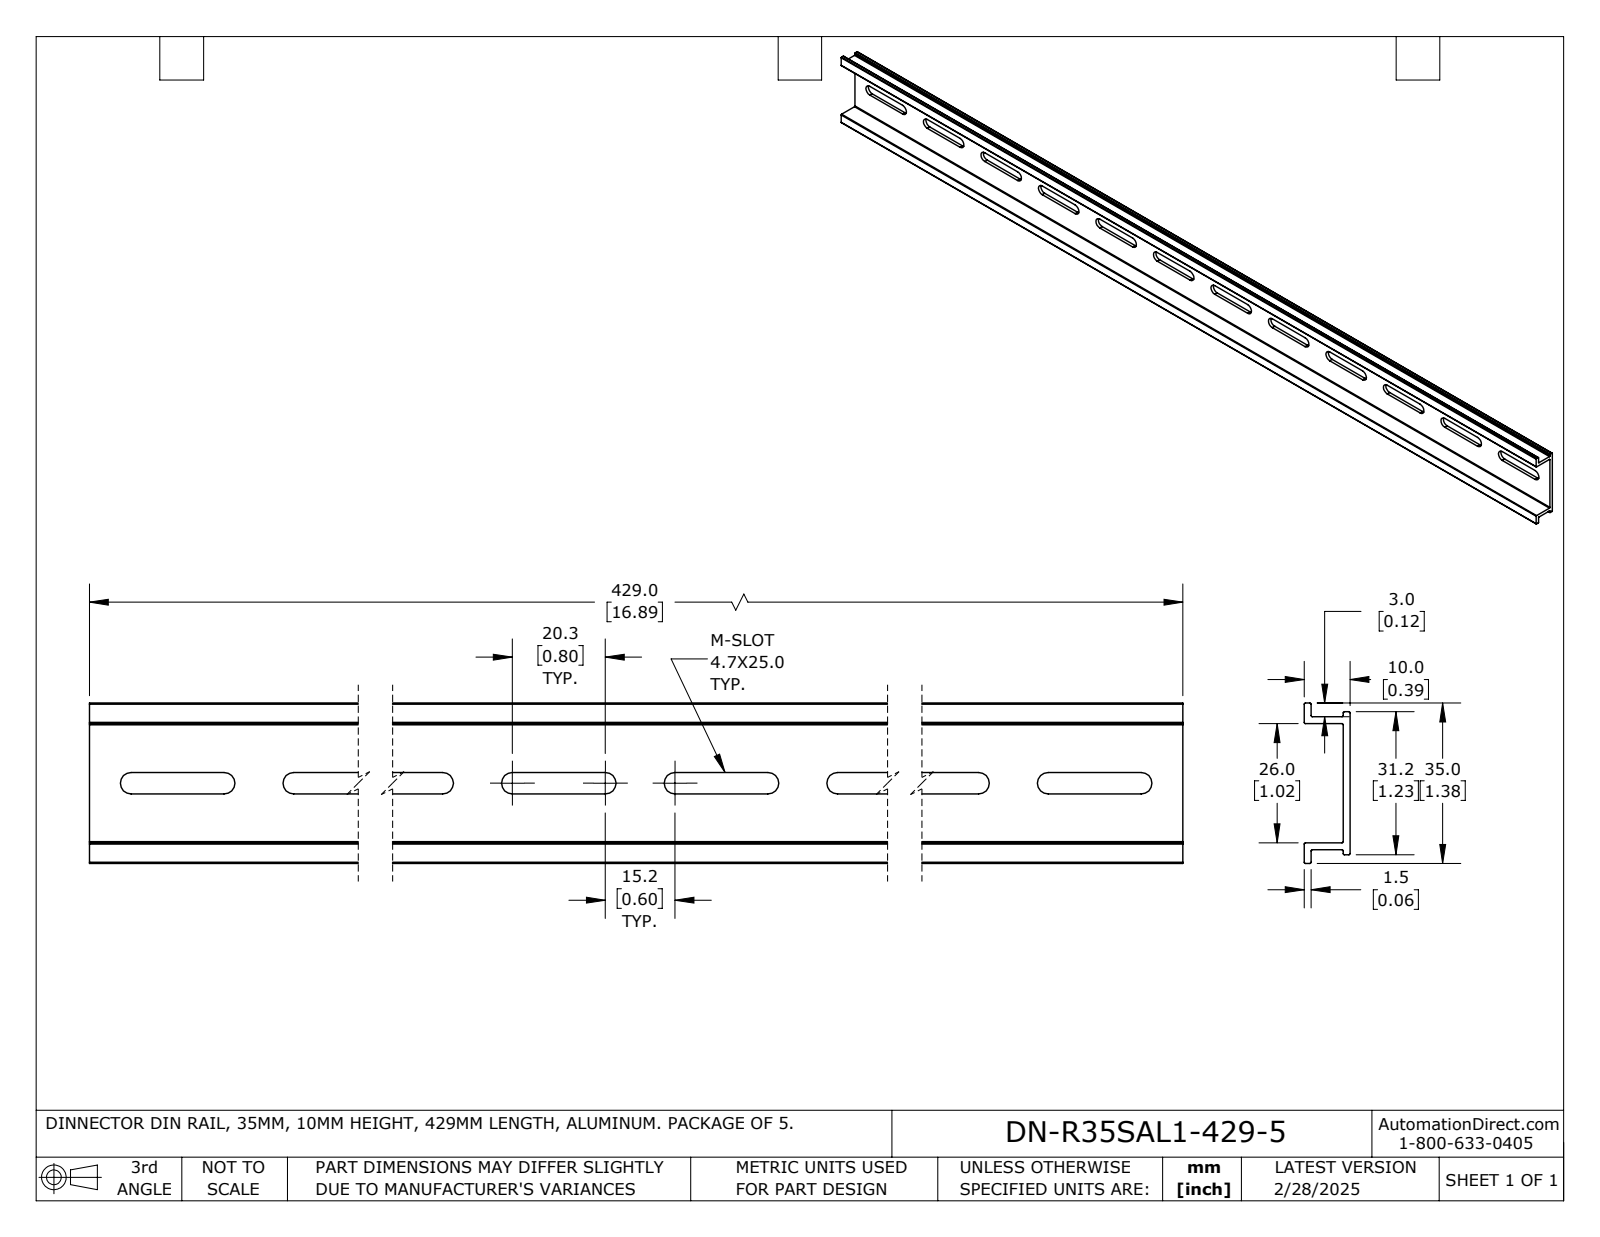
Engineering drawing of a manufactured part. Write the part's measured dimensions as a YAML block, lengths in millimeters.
part_name: "DN-R35SAL1-429-5_Default"
step_written_by: "SolidWorks 2024 (CONFIG_CONTROL_DESIGN)"
units: millimeters
bodies: {solids: 1, faces: 82, planar: 42, cylindrical: 40, other: 0}
overall_size: [429, 35, 10]
volume: 32822
surface_area: 45454
partial_cylinders:
  - {radius: 2.35, count: 24}
  - {radius: 0.27, count: 16}
face_to_face_distances: [1.5, 27.5, 8.5, 26, 10, 29, 7, 1.1, 2.6, 28.6]
